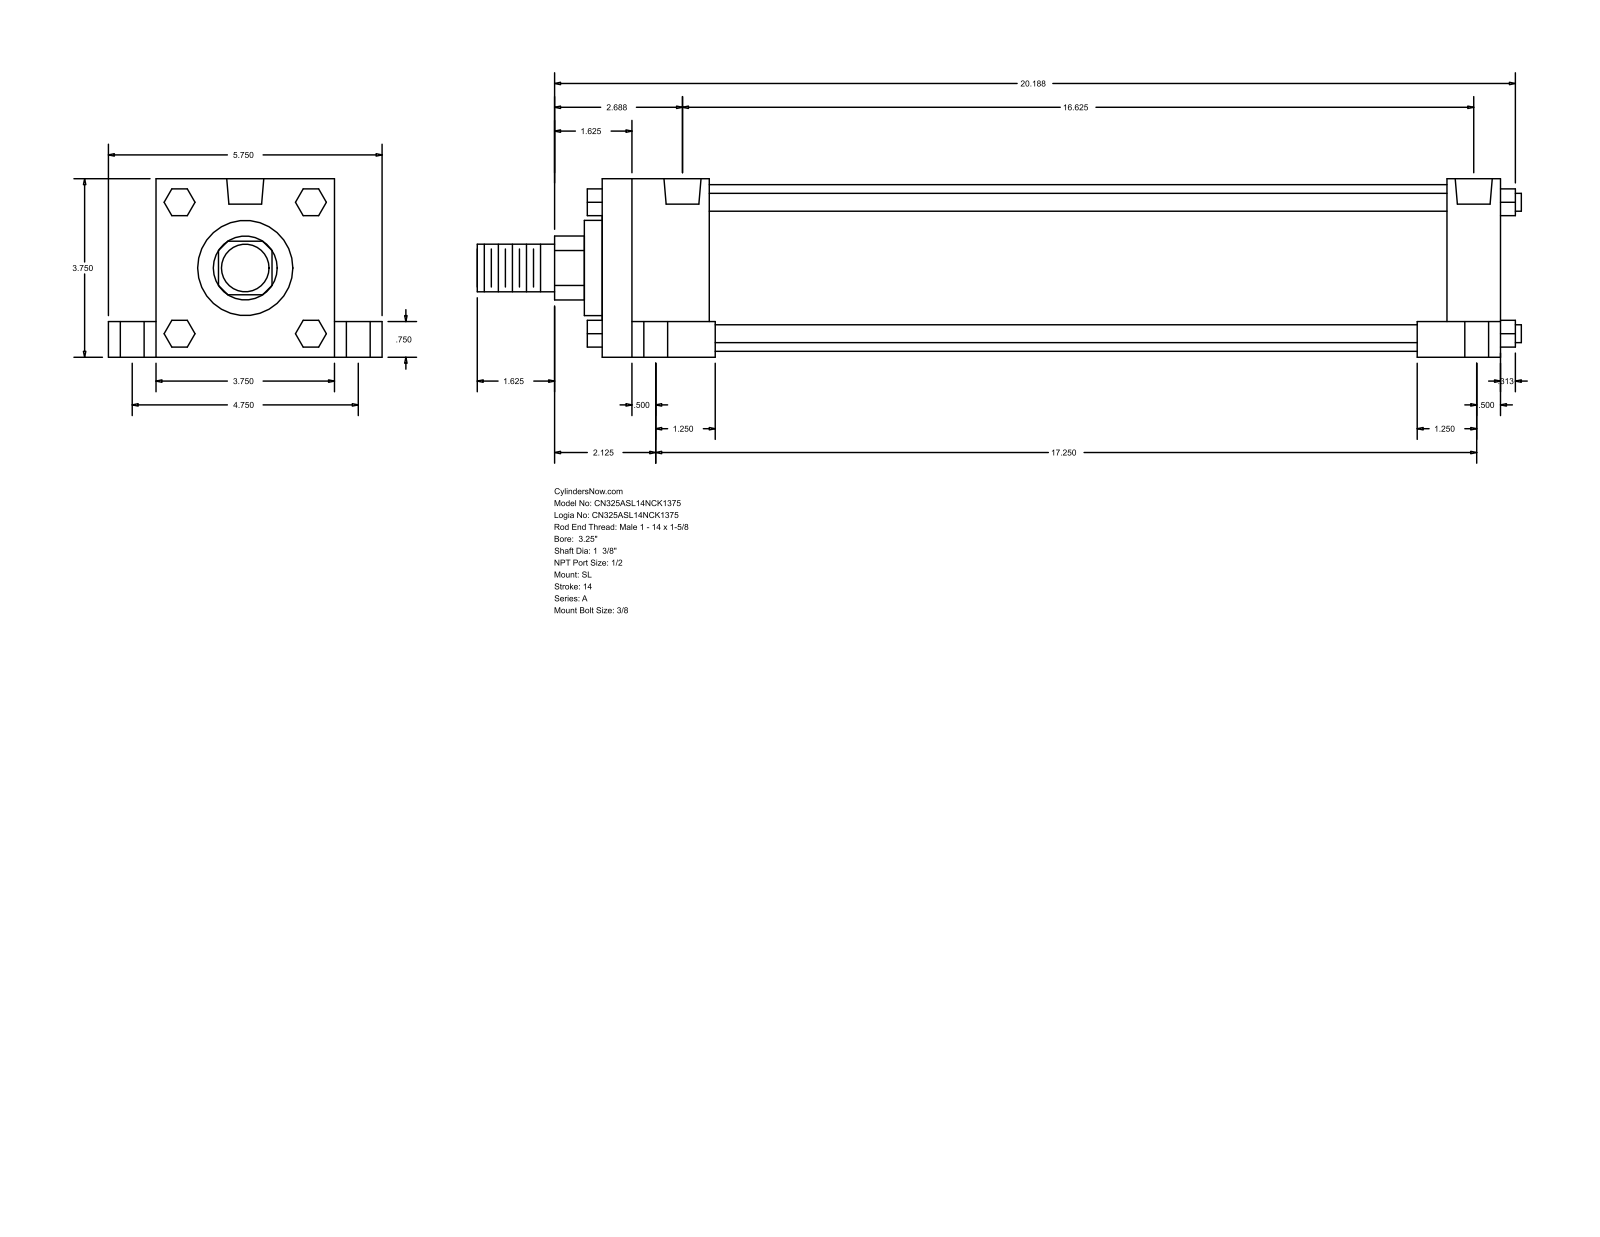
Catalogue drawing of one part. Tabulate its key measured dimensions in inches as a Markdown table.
| quantity | value |
| --- | --- |
| part name | A_SL__0325_1.375 |
| STEP written by | GSSL Pune (CONFIG_CONTROL_DESIGN) |
| units | inches |
| bodies | 0 solids, 150 faces (114 planar, 36 cylindrical, 0 other) |
| overall size | 21.937 × 5.75 × 3.75 |
| round holes (diameter × count) | 0.344 × 4, 0.5 × 4, 0.75 × 4, 0.778 × 2 |
| round bosses / shafts (diameter × count) | 0.375 × 4, 3.5 × 1, 2 × 1, 1.375 × 1, 1 × 1 |
| partial cylindrical surfaces (radius × count) | 0.672 × 1 |
| main face-to-face distances | 3.75, 18.875, 1, 4.75, 0.75, 3, 2.25, 1.125, 17.75, 15.5 |
| hole center spacings | 0.125, 2.376, 2.383, 2.441, 2.473, 4.75, 16.375, 16.5 |
